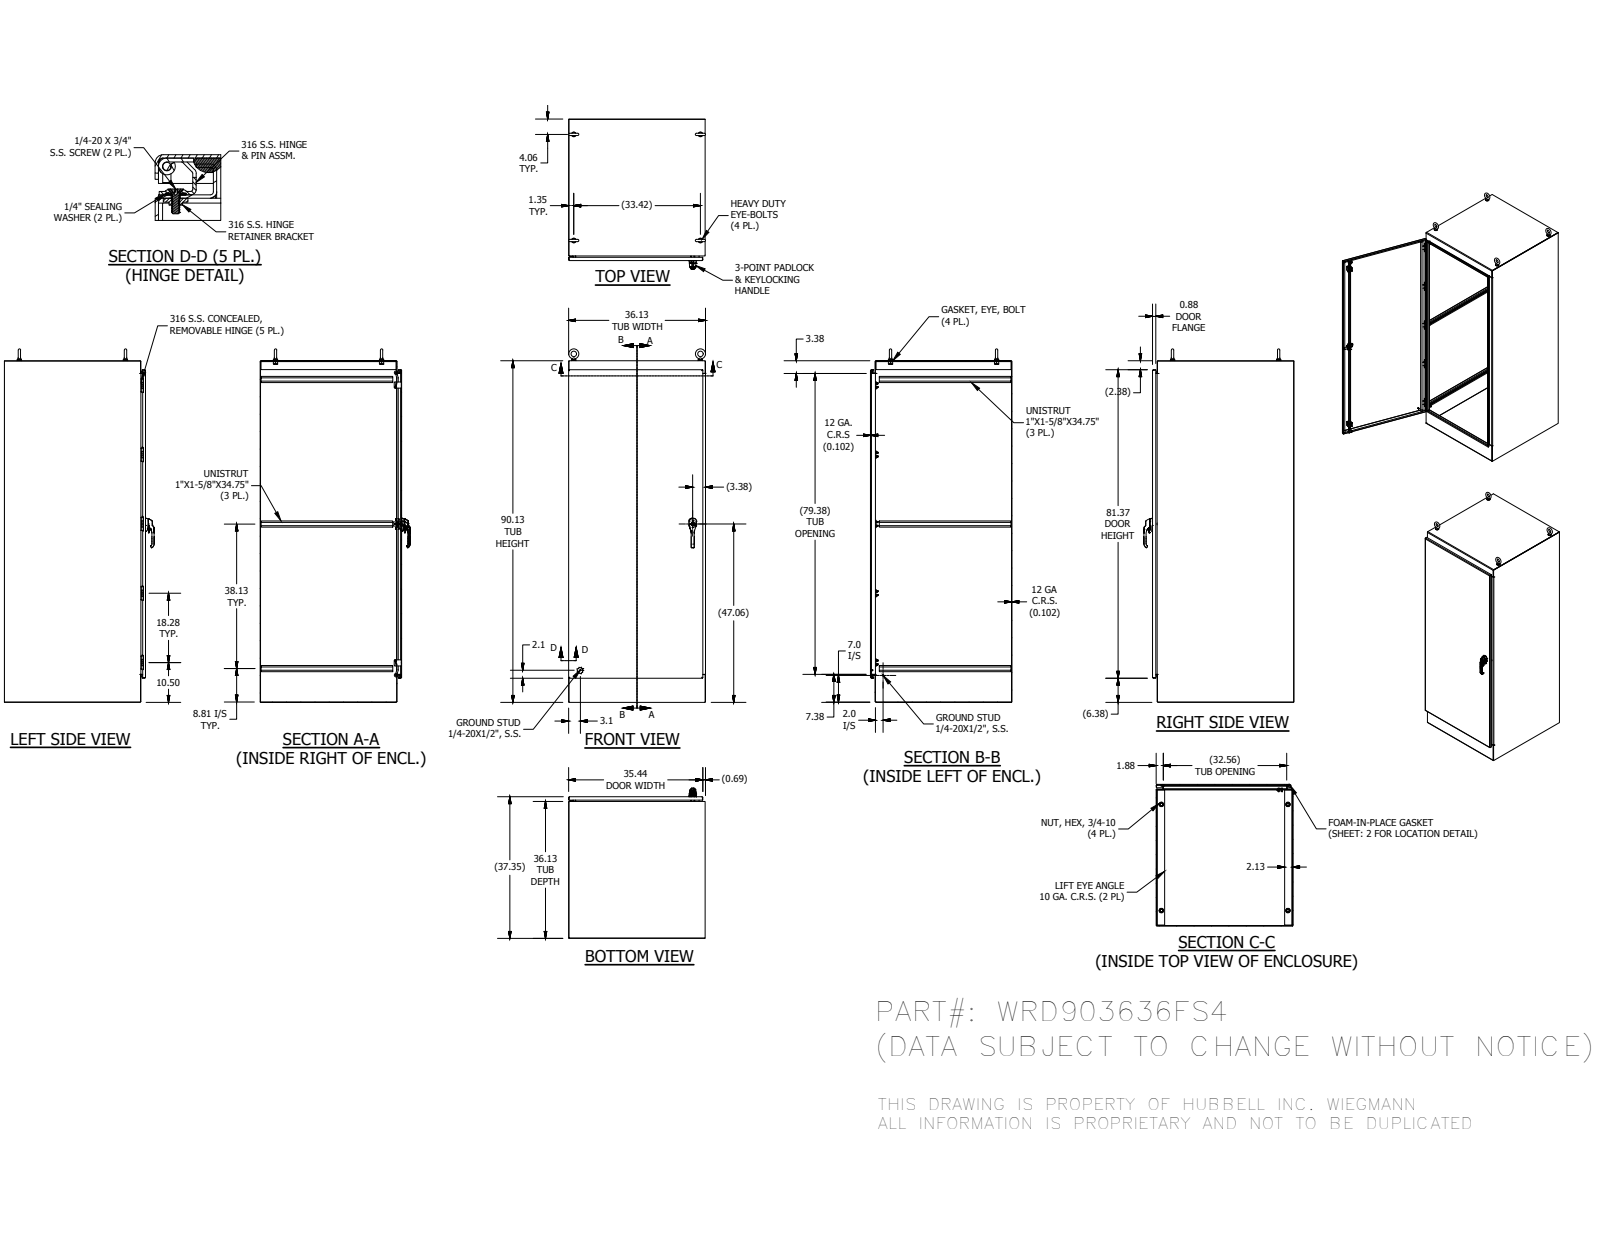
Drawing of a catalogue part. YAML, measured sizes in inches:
part_name: "WRD9036FS4FB; WRD3636FS4TOP; WRD3636FS4BTM; WRD9036FS4DR (+8 more)"
step_written_by: "Autodesk Inventor 2016 (AUTOMOTIVE_DESIGN)"
units: inches
bodies: {solids: 101, faces: 3975, planar: 1604, cylindrical: 1299, other: 1072}
overall_size: [93.248, 39.616, 36.127]
volume: 1887
surface_area: 36220
round_holes:
  - {diameter: 0.23, count: 10}
  - {diameter: 0.281, count: 10}
  - {diameter: 0.65, count: 10}
  - {diameter: 0.276, count: 8}
  - {diameter: 0.2, count: 4}
  - {diameter: 0.642, count: 4}
  - {diameter: 0.813, count: 4}
  - {diameter: 0.213, count: 3}
  - {diameter: 0.236, count: 3}
  - {diameter: 0.28, count: 3}
  - {diameter: 0.241, count: 2}
  - {diameter: 0.25, count: 2}
round_bosses_or_shafts:
  - {diameter: 0.25, count: 18}
  - {diameter: 0.625, count: 10}
  - {diameter: 0.404, count: 10}
  - {diameter: 0.182, count: 10}
  - {diameter: 1.25, count: 4}
  - {diameter: 1.12, count: 4}
  - {diameter: 0.75, count: 4}
  - {diameter: 1, count: 2}
partial_cylinders:
  - {radius: 0.02, count: 164}
  - {radius: 0.012, count: 86}
  - {radius: 0.063, count: 33}
  - {radius: 0.01, count: 26}
  - {radius: 0.125, count: 22}
  - {radius: 0.019, count: 19}
  - {radius: 0.079, count: 15}
  - {radius: 0.05, count: 14}
face_to_face_distances: [0.102, 36.023, 37.245, 35.921, 36.125, 37.143, 37.347, 90.023, 89.921, 90.125]
hole_center_spacings: [1, 0.492, 18.281, 18.281, 36.563, 54.844, 0.256, 0.886]
